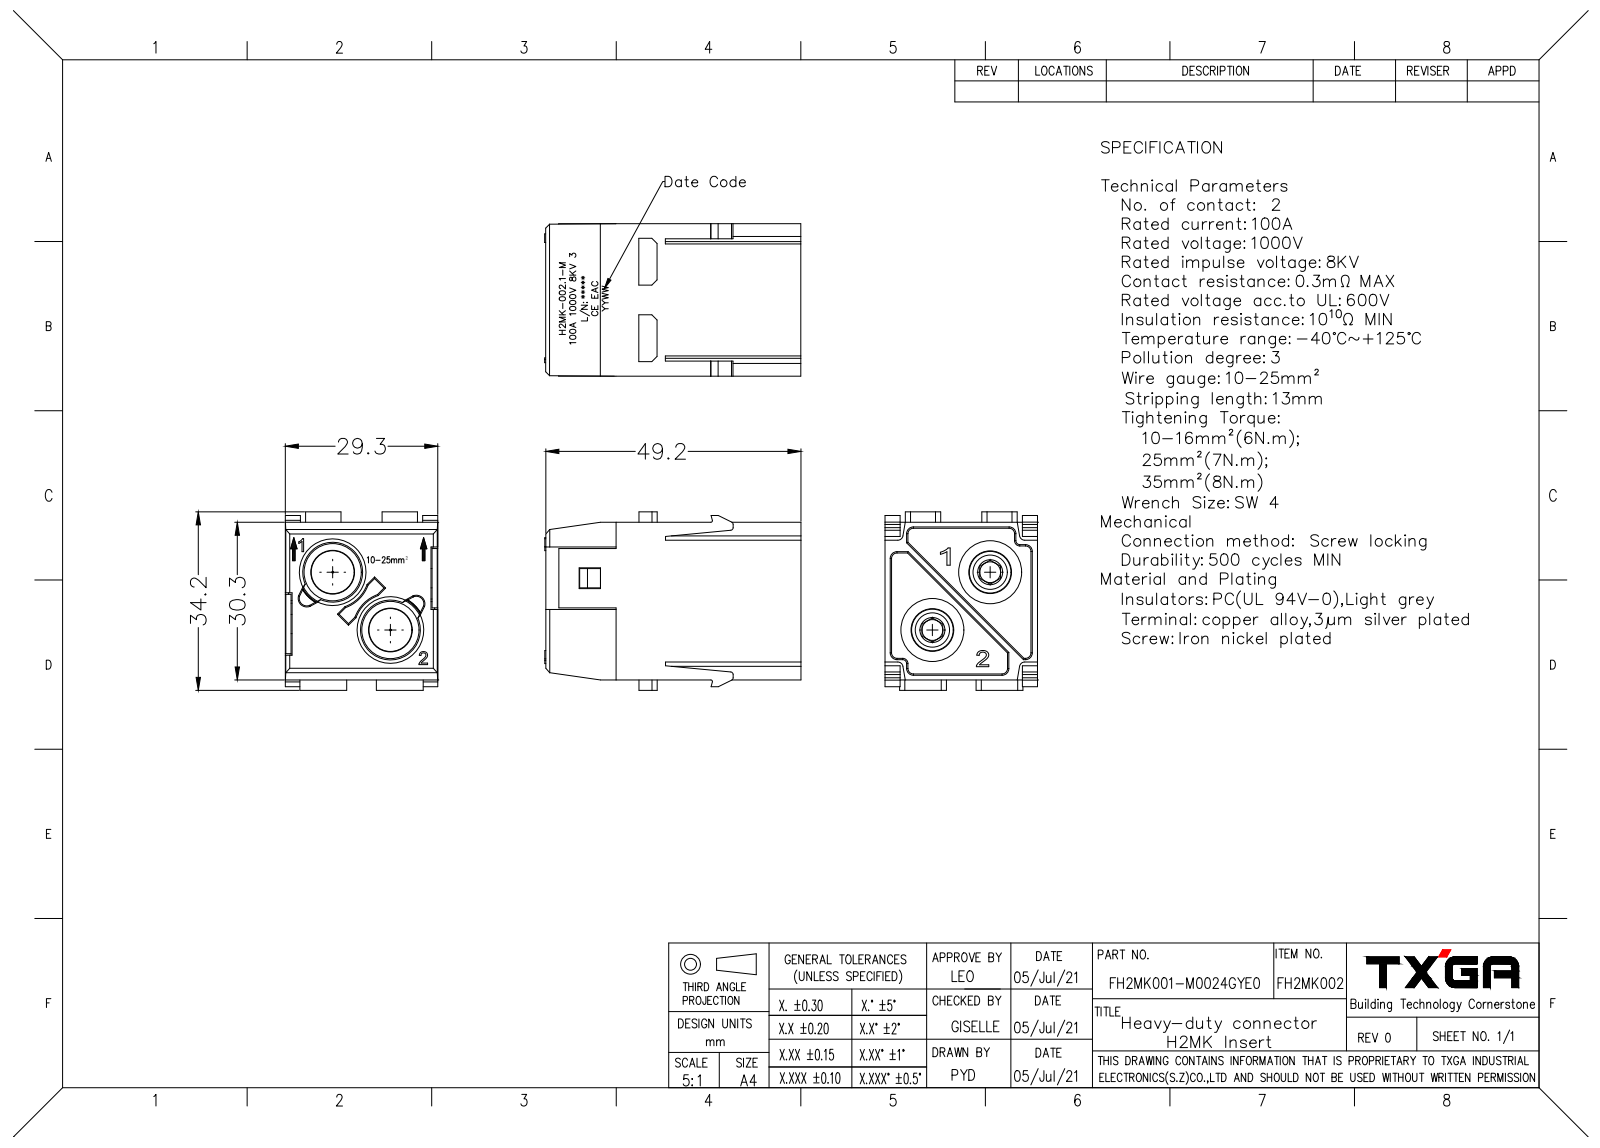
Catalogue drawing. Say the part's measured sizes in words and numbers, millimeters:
The part is named "FH2MK001-M0024GYE0 H2MK-002.1-M". Its 3-D file was written by "SolidWorks 2021 (CONFIG_CONTROL_DESIGN)". It is 1 solid with 548 faces: 352 planar, 100 cylindrical and 96 other. Overall it measures 49.23 by 34.3 by 29.3 millimeters. Its volume is 22 958 cubic millimeters and its surface area 28 583 square millimeters. Round holes: 2 of diameter 4, 2 of diameter 4.8, 2 of diameter 7.2, 2 of diameter 8, 2 of diameter 8.2, 2 of diameter 8.4, 2 of diameter 12, 2 of diameter 12.1, 2 of diameter 13.3. Round bosses or shafts: 3 of diameter 2.3, 2 of diameter 13, 2 of diameter 8.25, 2 of diameter 7.95, 2 of diameter 7.55, 2 of diameter 6.65, 2 of diameter 6.05. Partial cylindrical surfaces (rounded edges, fillets, slot ends): 14 of radius 0.5, 6 of radius 1, 4 of radius 1.55, 3 of radius 1.35, 2 of radius 0.3, 2 of radius 2, 2 of radius 8.6, 1 of radius 1.6. The main face-to-face distances are 29.3, 1.3, 28, 30.3, 1.1, 28.2, 1, 26.9, 29, 34.53. The hole center spacings are 15.7.
